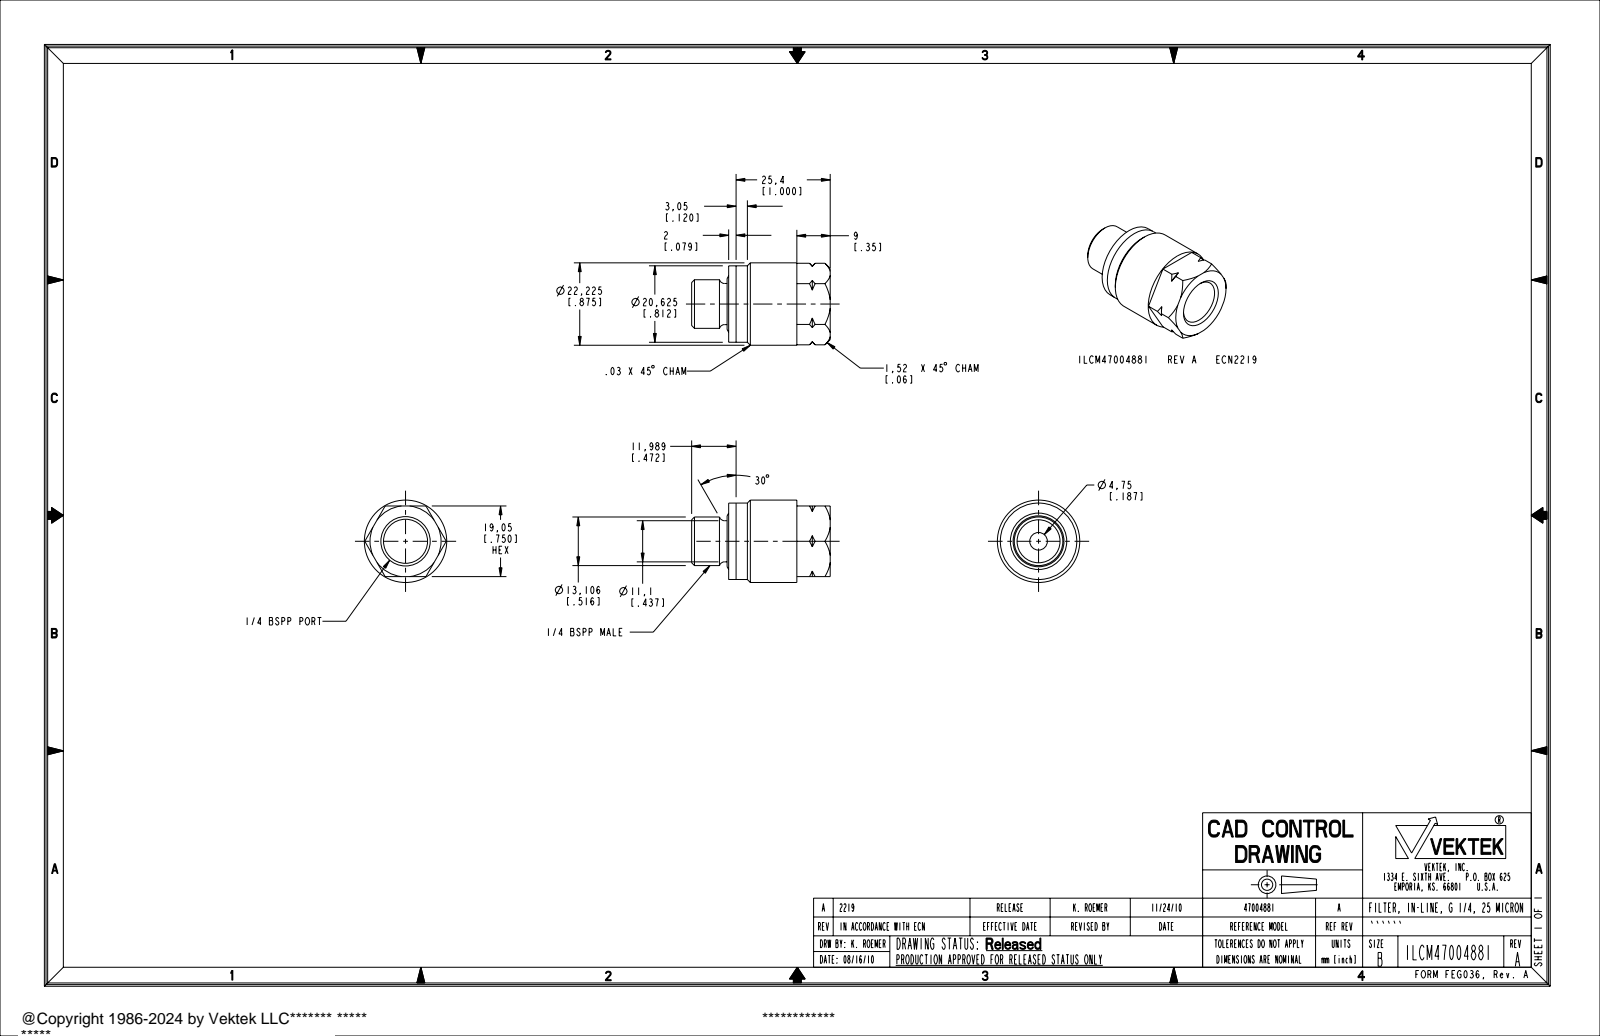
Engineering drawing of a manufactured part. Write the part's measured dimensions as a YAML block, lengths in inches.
part_name: "ILCM47004881"
step_written_by: "PRO/ENGINEER BY PARAMETRIC TECHNOLOGY CORPORATION, 2007460 (AUTOMOTIVE_DESIGN_CC2)"
units: inches
bodies: {solids: 1, faces: 64, planar: 14, cylindrical: 16, other: 34}
overall_size: [1.472, 0.875, 0.875]
volume: 0.553
surface_area: 6.025
round_holes:
  - {diameter: 0.187, count: 1}
  - {diameter: 0.468, count: 1}
  - {diameter: 0.541, count: 1}
round_bosses_or_shafts:
  - {diameter: 0.875, count: 1}
  - {diameter: 0.812, count: 1}
  - {diameter: 0.811, count: 1}
  - {diameter: 0.516, count: 1}
  - {diameter: 0.437, count: 1}
face_to_face_distances: [0.75, 1.079, 0.548, 0.531, 0.75, 0.393, 0.941, 1.472, 1.118, 0.724]
